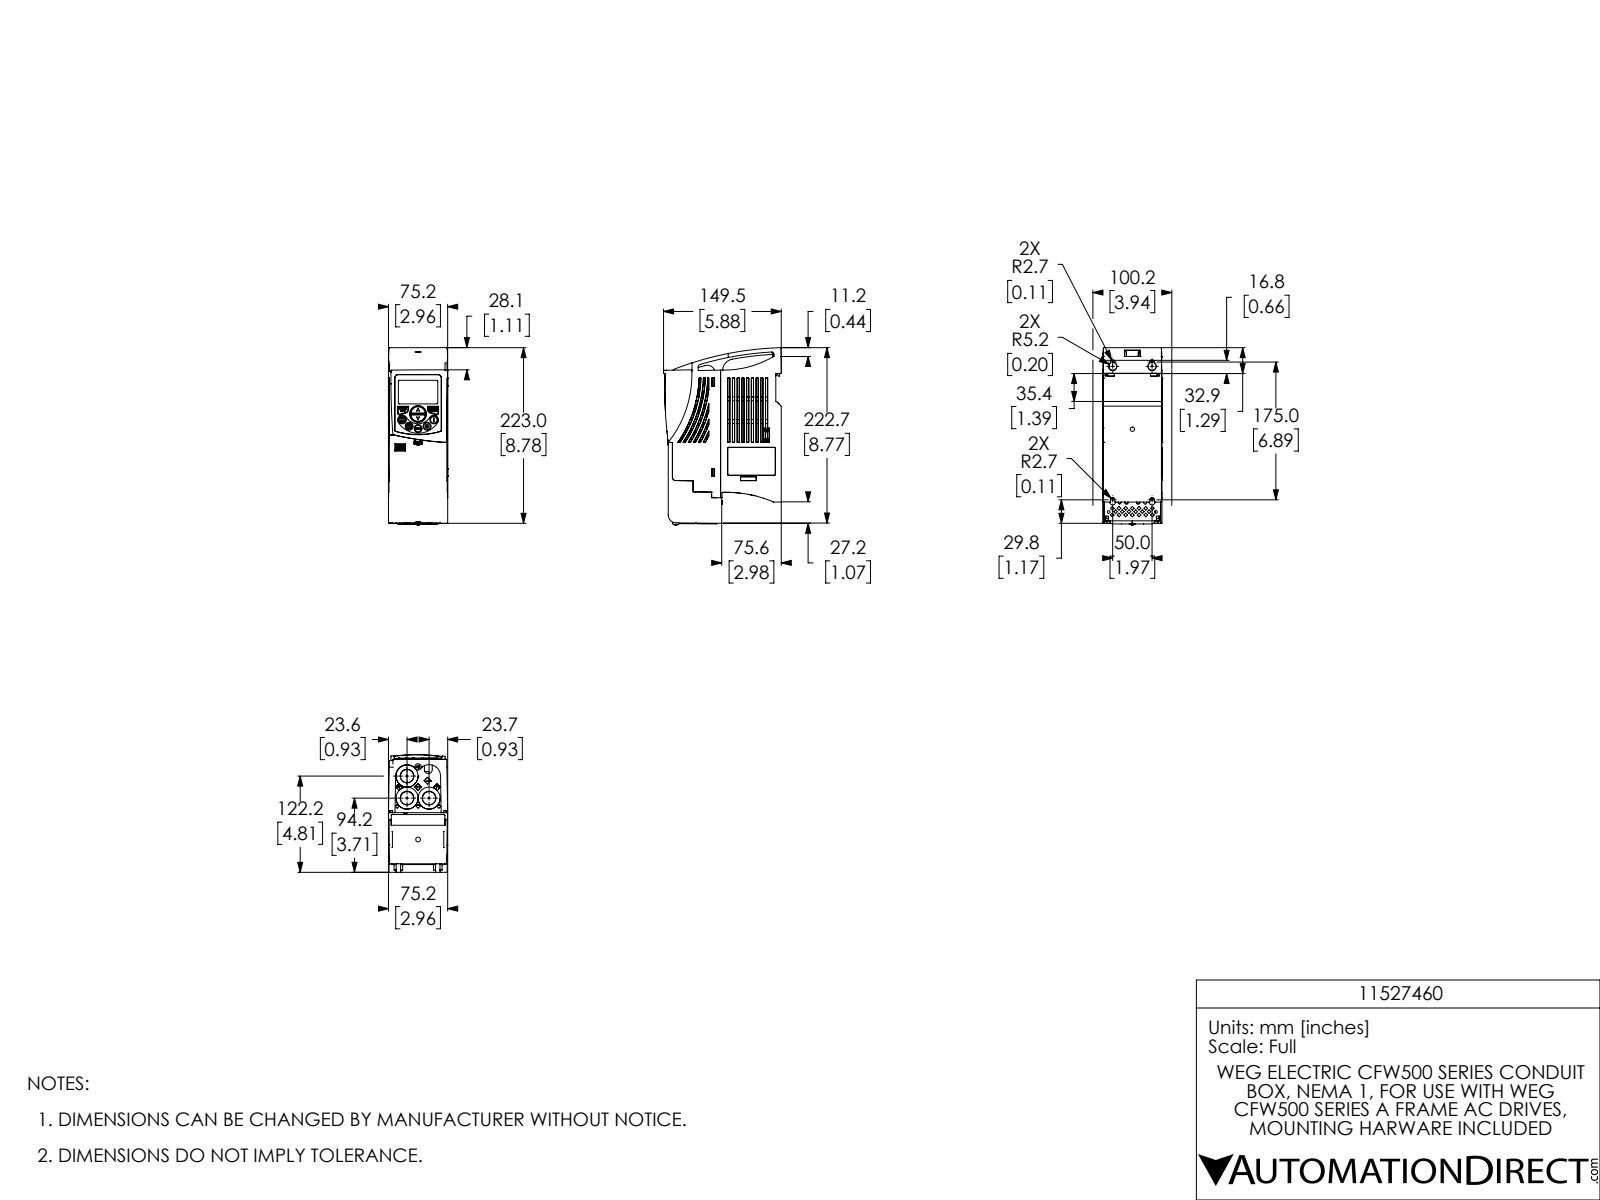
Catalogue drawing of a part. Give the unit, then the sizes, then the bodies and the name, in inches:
Units: inches
Overall size (bounding box): 8.858 × 5.885 × 2.962
Round holes (diameter × count): ⌀0.138 ×7, ⌀0.173 ×4, ⌀0.394 ×3, ⌀0.669 ×3, ⌀0.886 ×3, ⌀0.098 ×2, ⌀0.165 ×2, ⌀0.177 ×2, ⌀0.386 ×2, ⌀0.214 ×1, ⌀0.787 ×1, ⌀0.846 ×1
Round bosses / shafts (diameter × count): ⌀1.102 ×3, ⌀1.024 ×3, ⌀0.394 ×2, ⌀0.315 ×2, ⌀0.26 ×2, ⌀0.157 ×2, ⌀1.181 ×1, ⌀0.197 ×1
Partial cylindrical surfaces — rounded edges, fillets, slot ends (radius × count): R0.012 ×171, R0.01 ×104, R0.008 ×91, R0.02 ×59, R0.039 ×26, R0.098 ×10, R0.118 ×7, R0.079 ×6
Main face-to-face distances: 0.122, 3.031, 0.059, 0.079, 0.02, 0.102, 5.65, 2.618, 0.121, 0.063
Hole centre spacings: 0.079, 0.157, 0.236, 0.315, 0.935, 0.394, 0.472, 0.551
Volume: 69.14 in³ · Surface area: 444 in²
Bodies: 20 solids, 5675 faces (2923 planar, 1015 cylindrical, 1737 other)
Part name (STEP PRODUCT): 11527460 b
STEP written by: SolidWorks 2017 (AUTOMOTIVE_DESIGN)
